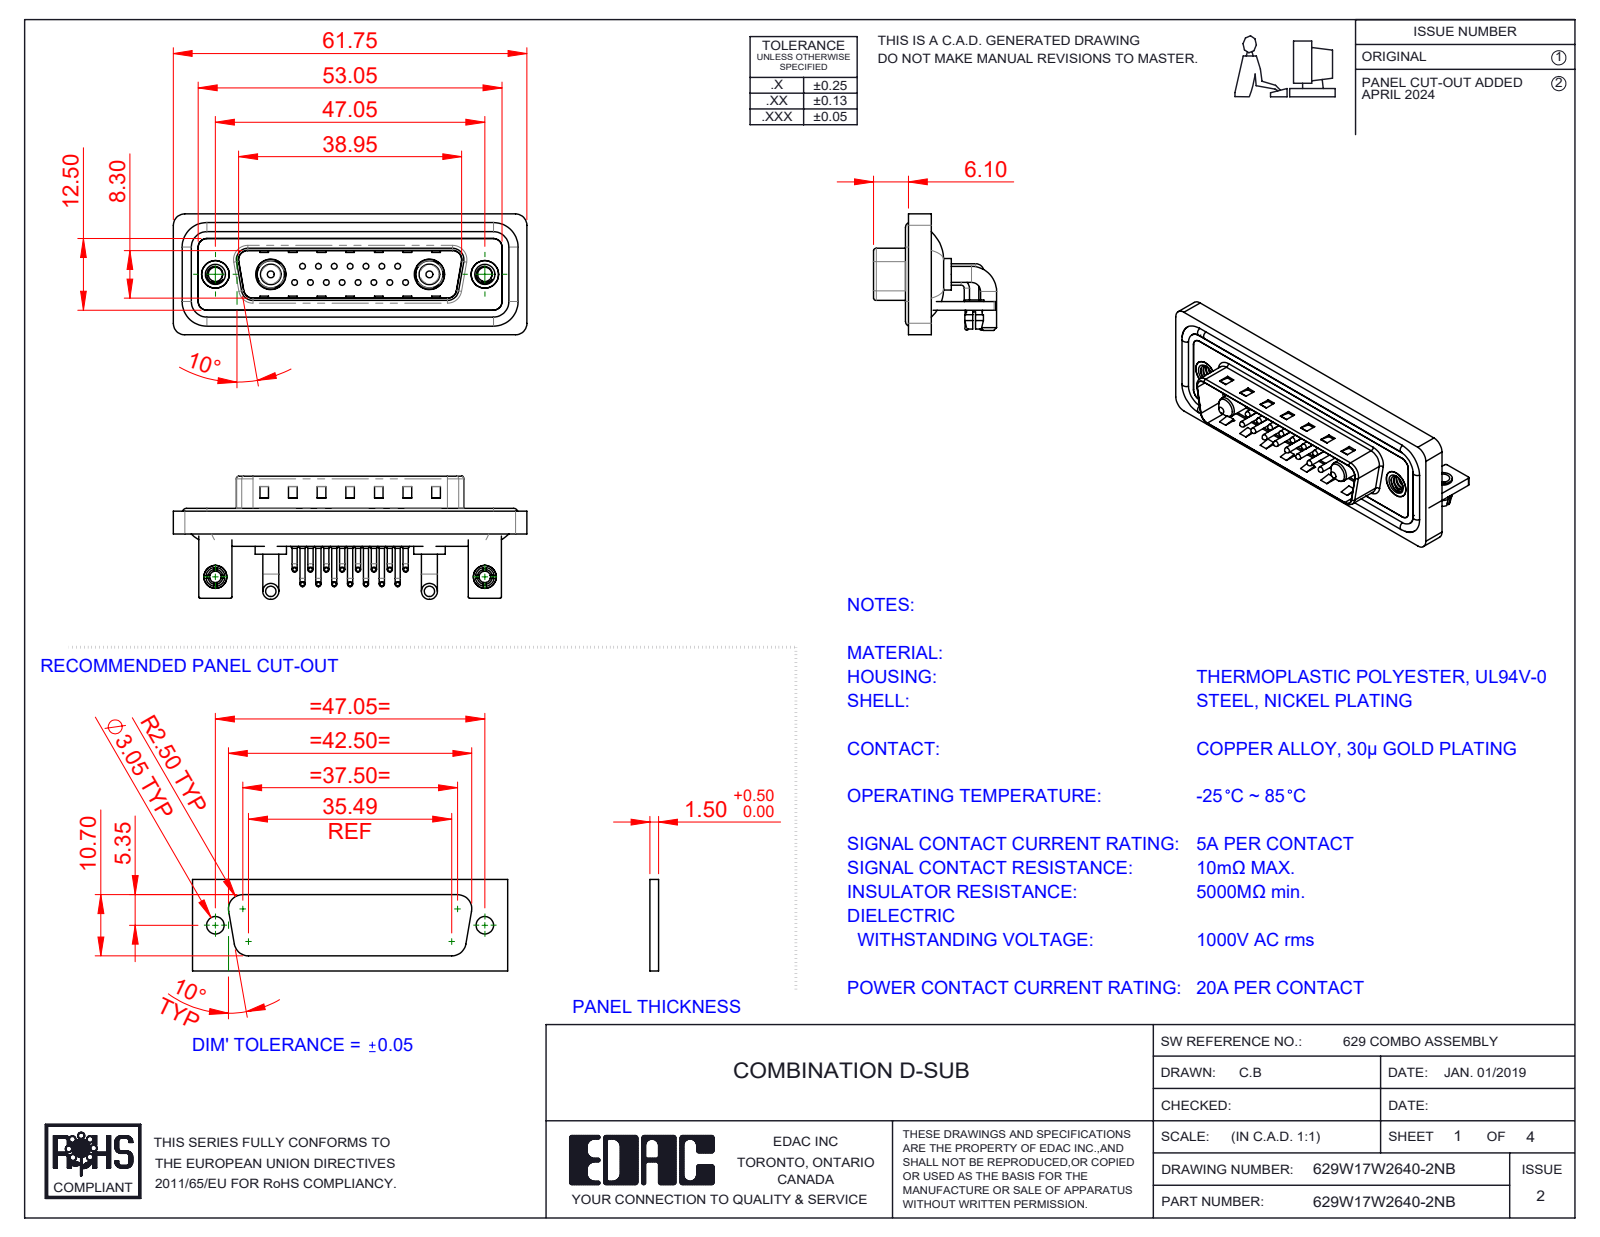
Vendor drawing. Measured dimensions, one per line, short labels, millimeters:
name: 629Combo Waterproof Housing_25 Contacts; 629Combo Threaded Rivet_B; 629Combo Board Lock; 629W17W2640-2NB (+7 more)
written by: SolidWorks 2023 (CONFIG_CONTROL_DESIGN)
unit: mm
bodies: 30 solids, 2349 faces (1257 planar, 820 cylindrical, 272 other)
size: 61.75 × 21.5 × 21.1
volume: 7 820 mm³; area: 13 399 mm²
holes: 17× ⌀2, 15× ⌀0.75, 15× ⌀1.6, 4× ⌀2.5, 2× ⌀3.2, 2× ⌀4, 2× ⌀4.8, 2× ⌀4.85, 2× ⌀5, 2× ⌀5.3
bosses: 30× ⌀0.9, 15× ⌀1.5, 15× ⌀1, 15× ⌀0.65, 4× ⌀2.8, 4× ⌀1.6, 2× ⌀5.5, 2× ⌀5.2
rounds: 19× R2, 18× R1.5, 16× R0.25, 15× R1.01, 9× R0.5, 8× R1.6, 4× R0.6, 4× R0.65
face distances: 0.4, 0.8, 1.5, 2.1, 2.9, 1.1, 4.1, 1.6, 4.5, 3.7
hole spacings: 3.16, 2.77, 5.54, 8.31, 5.04, 7.49, 11.08, 5.03
